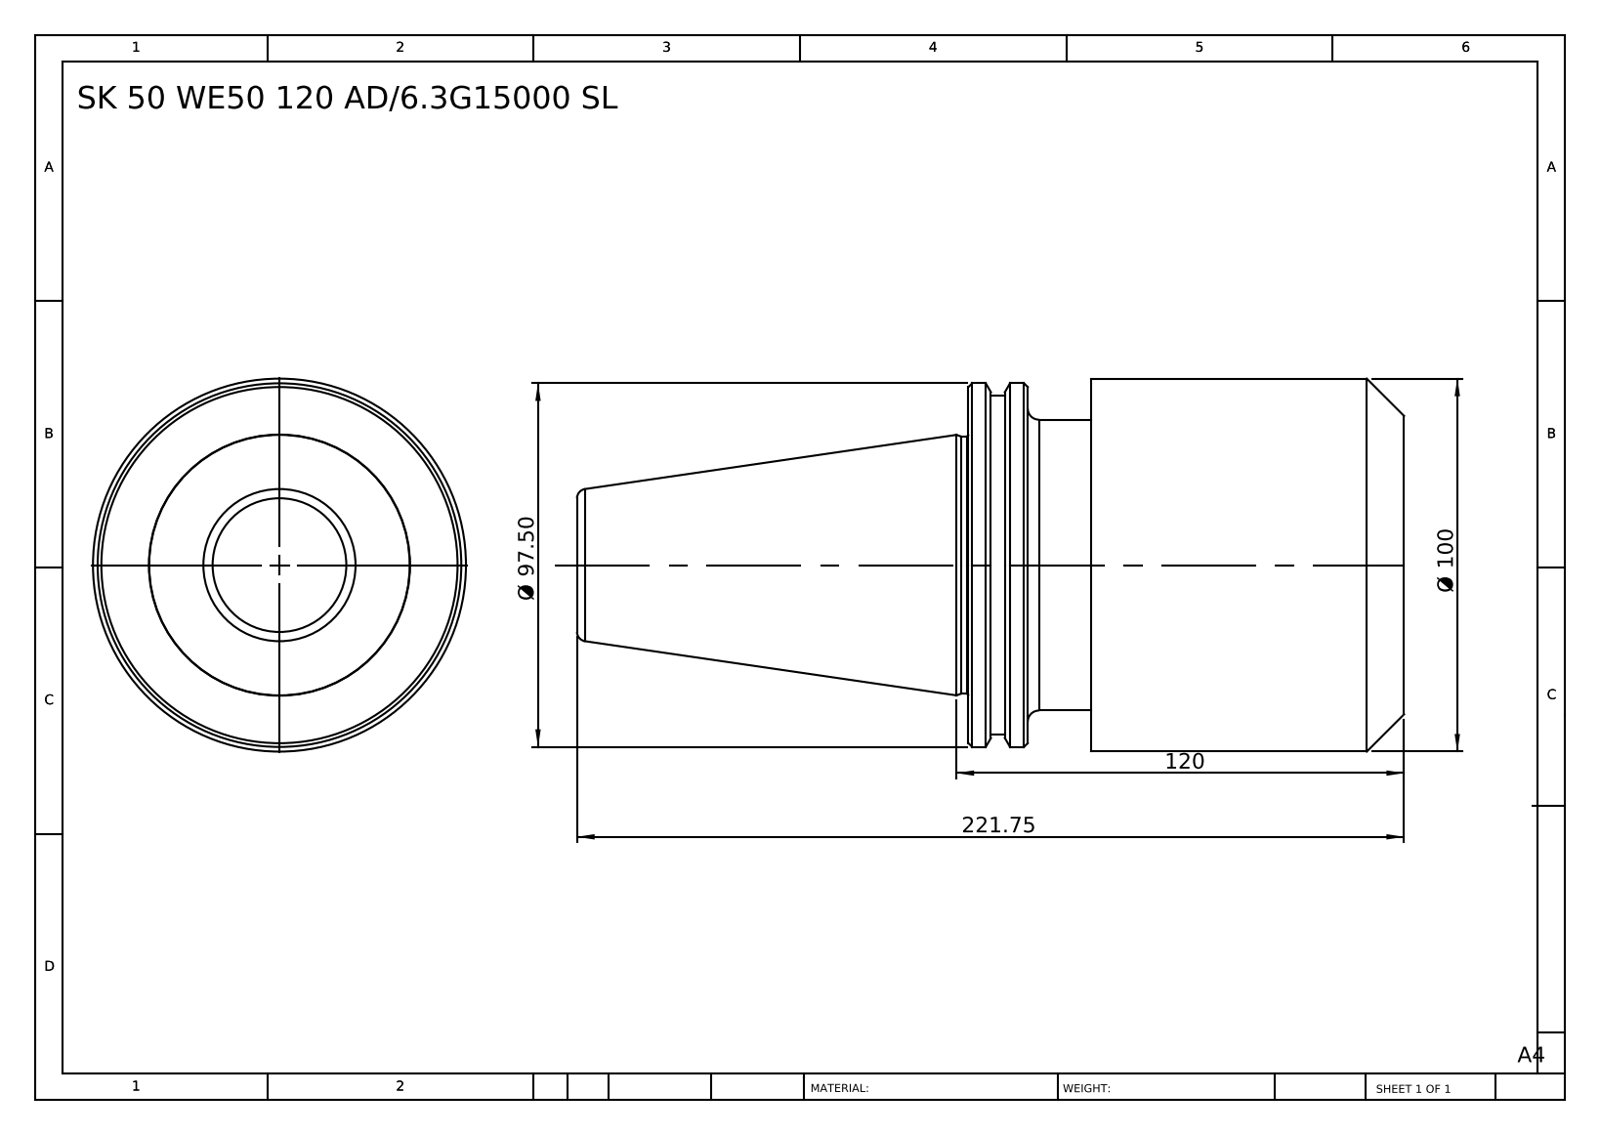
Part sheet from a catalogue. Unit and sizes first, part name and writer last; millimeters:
Units: millimetres
Overall size (bounding box): 221.75 × 100 × 100
Round bosses / shafts (diameter × count): ⌀100 ×1, ⌀97.5 ×1, ⌀91 ×1, ⌀78 ×1, ⌀69 ×1
Main face-to-face distances: 116.8, 83.9, 32.9, 100.9, 17, 15.9, 221.75, 137.85, 120.85, 104.95
Volume: 1 099 000 mm³ · Surface area: 70 927 mm²
Bodies: 1 solid, 39 faces (7 planar, 12 cylindrical, 20 other)
Part name (STEP PRODUCT): SK50 WE50 120 AD-6.3G15000 SL
STEP written by: SolidWorks 2014 (CONFIG_CONTROL_DESIGN)
